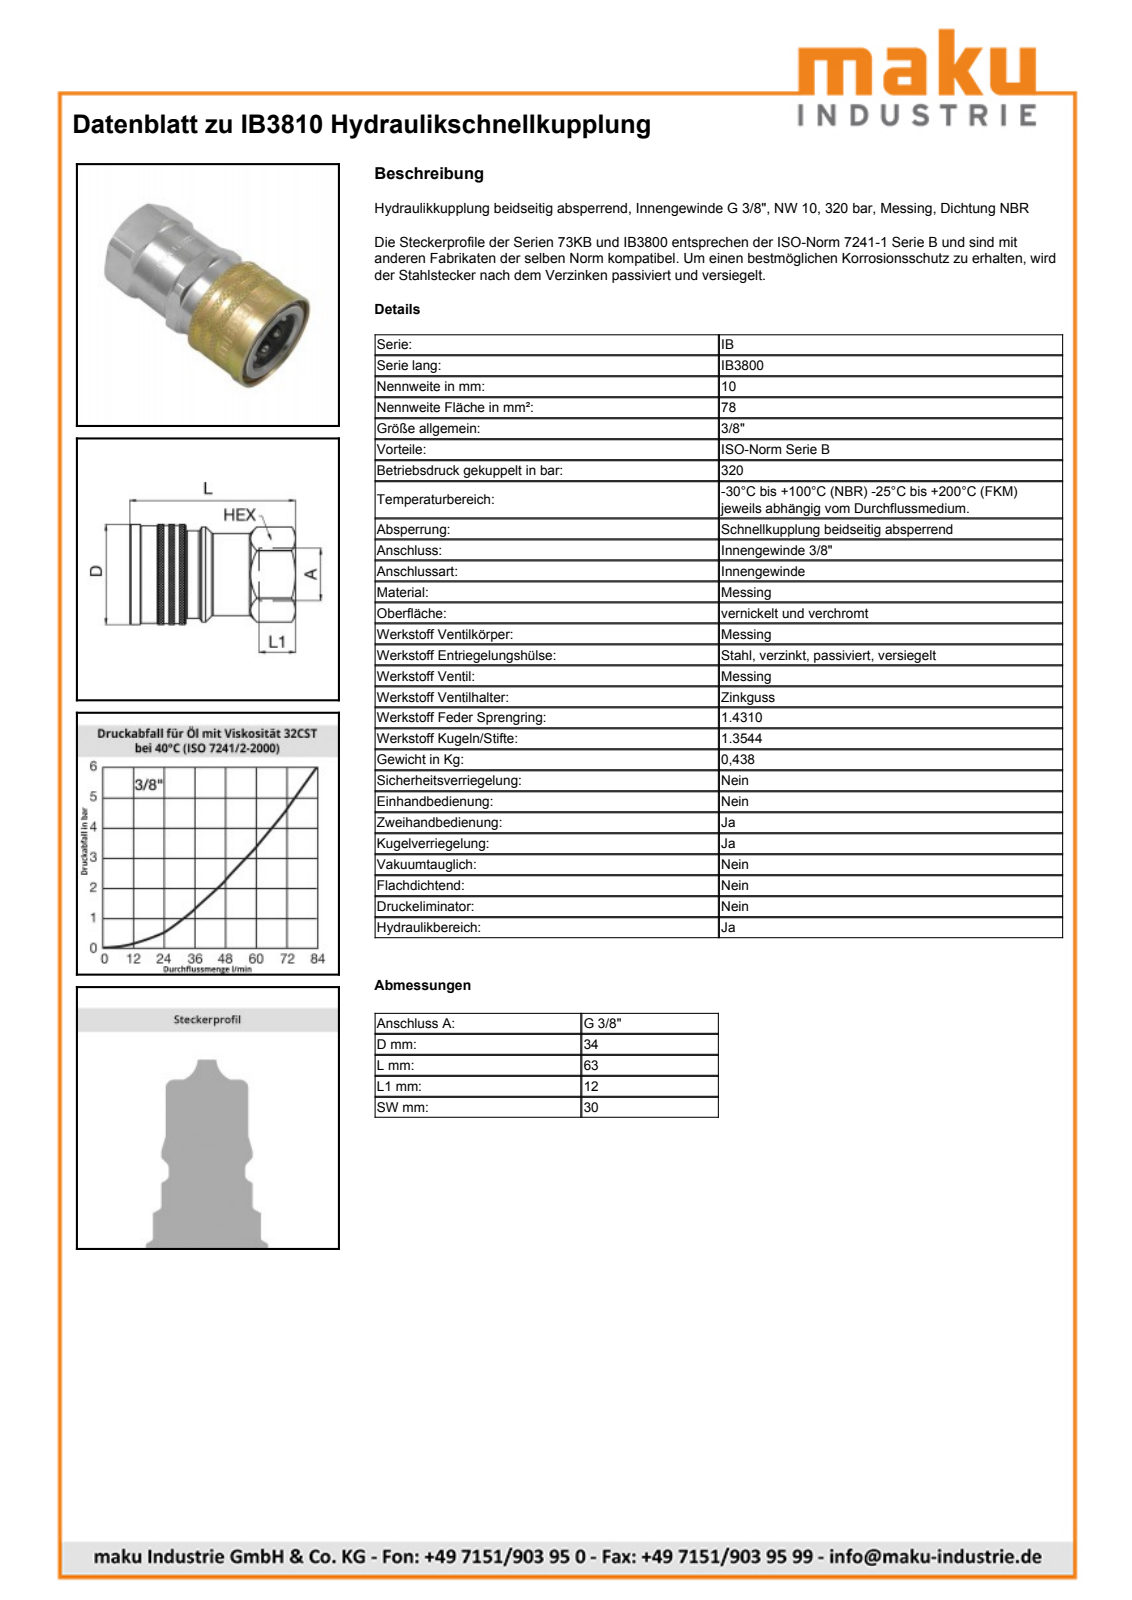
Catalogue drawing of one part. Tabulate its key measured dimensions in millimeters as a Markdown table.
| quantity | value |
| --- | --- |
| part name | IB3810 |
| STEP written by | SolidWorks 2009 (AUTOMOTIVE_DESIGN) |
| units | millimeters |
| bodies | 2 solids, 274 faces (39 planar, 79 cylindrical, 156 other) |
| overall size | 62.5 × 34 × 34 |
| volume | 38 392 mm³ |
| surface area | 13 145 mm² |
| round holes (diameter × count) | 10 × 1, 14.95 × 1, 19.1 × 1, 19.5 × 1, 20.1 × 1, 21.7 × 1, 27.8 × 1, 30.8 × 1, 31.2 × 1 |
| round bosses / shafts (diameter × count) | 34 × 1, 33.2 × 1, 33 × 1, 29.6 × 1, 27.6 × 1, 26.1 × 1 |
| partial cylindrical surfaces (radius × count) | 11.14 × 1, 15.3 × 1 |
| main face-to-face distances | 30, 62.5, 2, 12.84, 49.66, 38, 25.16, 24.5, 0.9, 8 |
